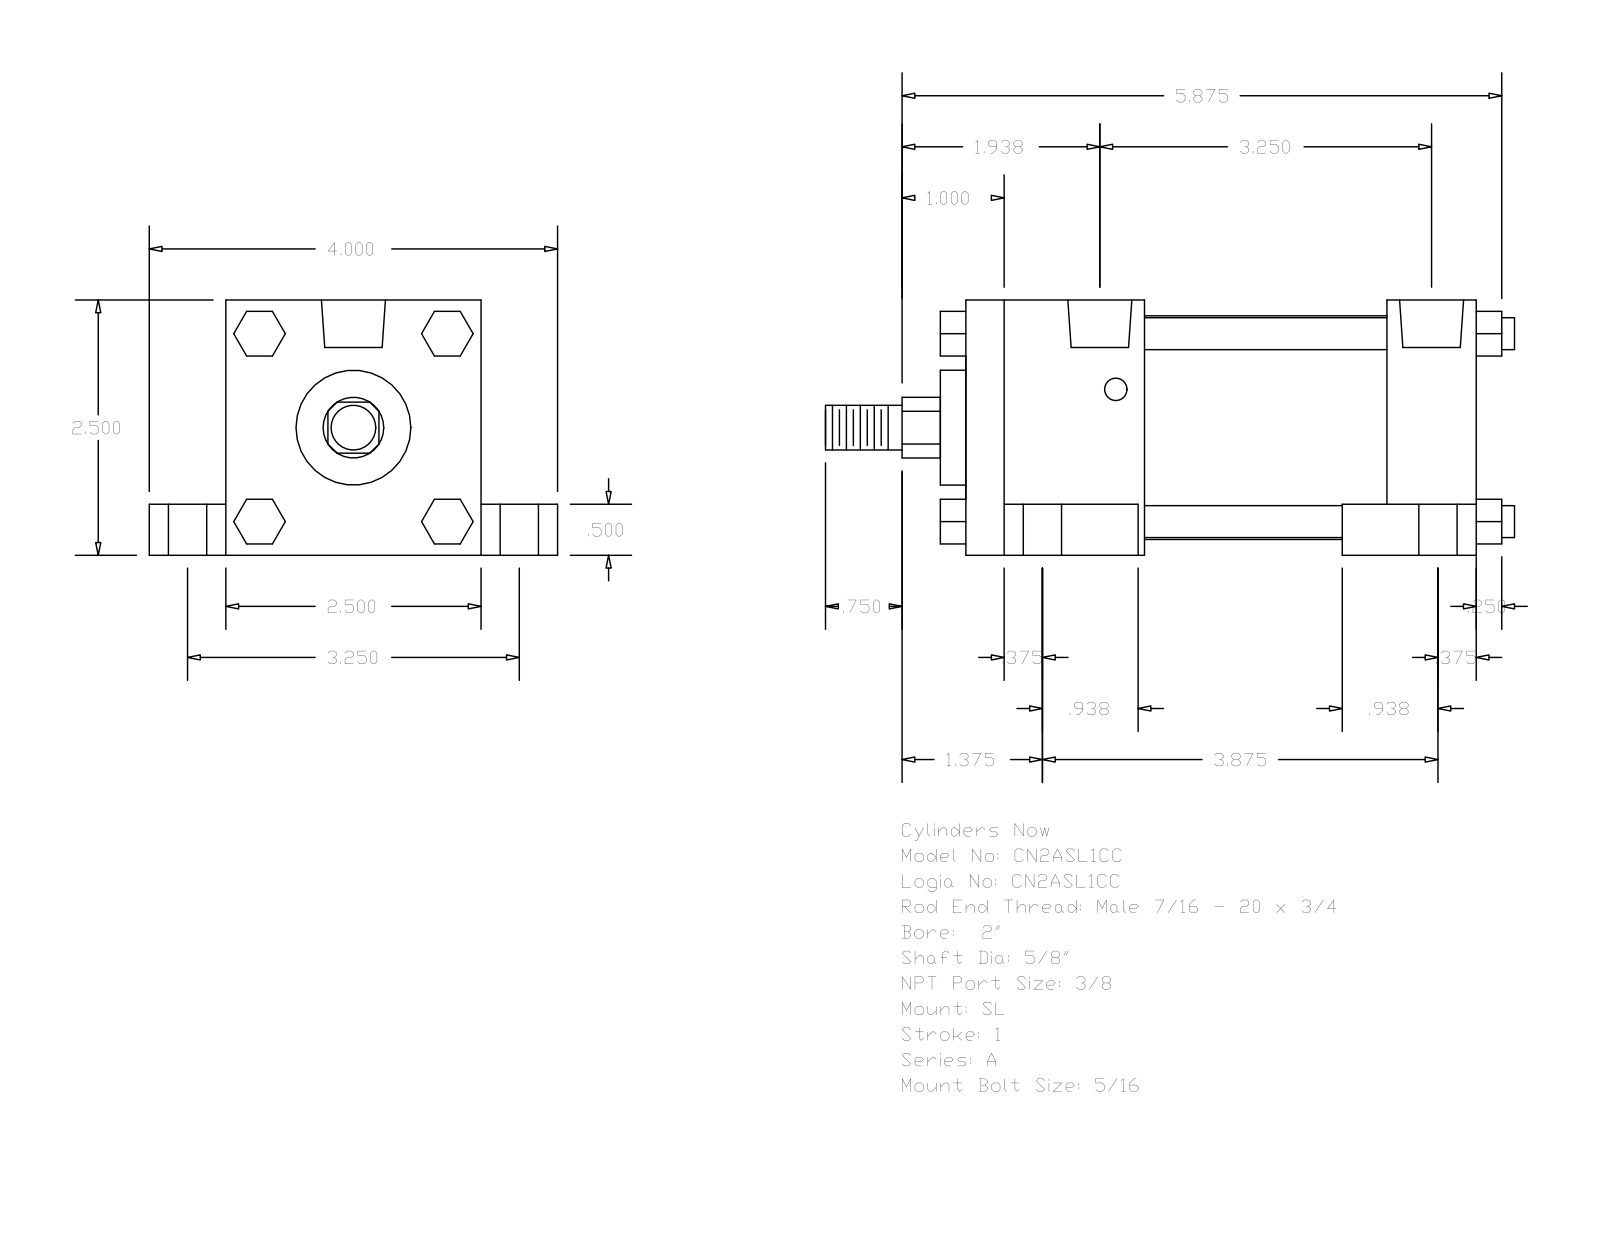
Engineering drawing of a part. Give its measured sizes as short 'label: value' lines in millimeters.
name: A_SL__0200_0.625
written by: GSSL Pune (CONFIG_CONTROL_DESIGN)
unit: mm
bodies: 0 solids, 148 faces (112 planar, 36 cylindrical, 0 other)
size: 171.45 × 101.6 × 63.5
holes: 4× ⌀5.56, 4× ⌀9.53, 4× ⌀15.88, 2× ⌀15.93
bosses: 4× ⌀7.94, 1× ⌀55.63, 1× ⌀28.57, 1× ⌀15.88, 1× ⌀11.11
rounds: 1× R7.54
face distances: 63.5, 127, 82.55, 50.8, 12.7, 19.05, 44.45, 104.77, 60.32, 22.23
hole spacings: 41.3, 41.64, 43.67, 45.13, 74.6, 82.54, 90.16, 93.72
